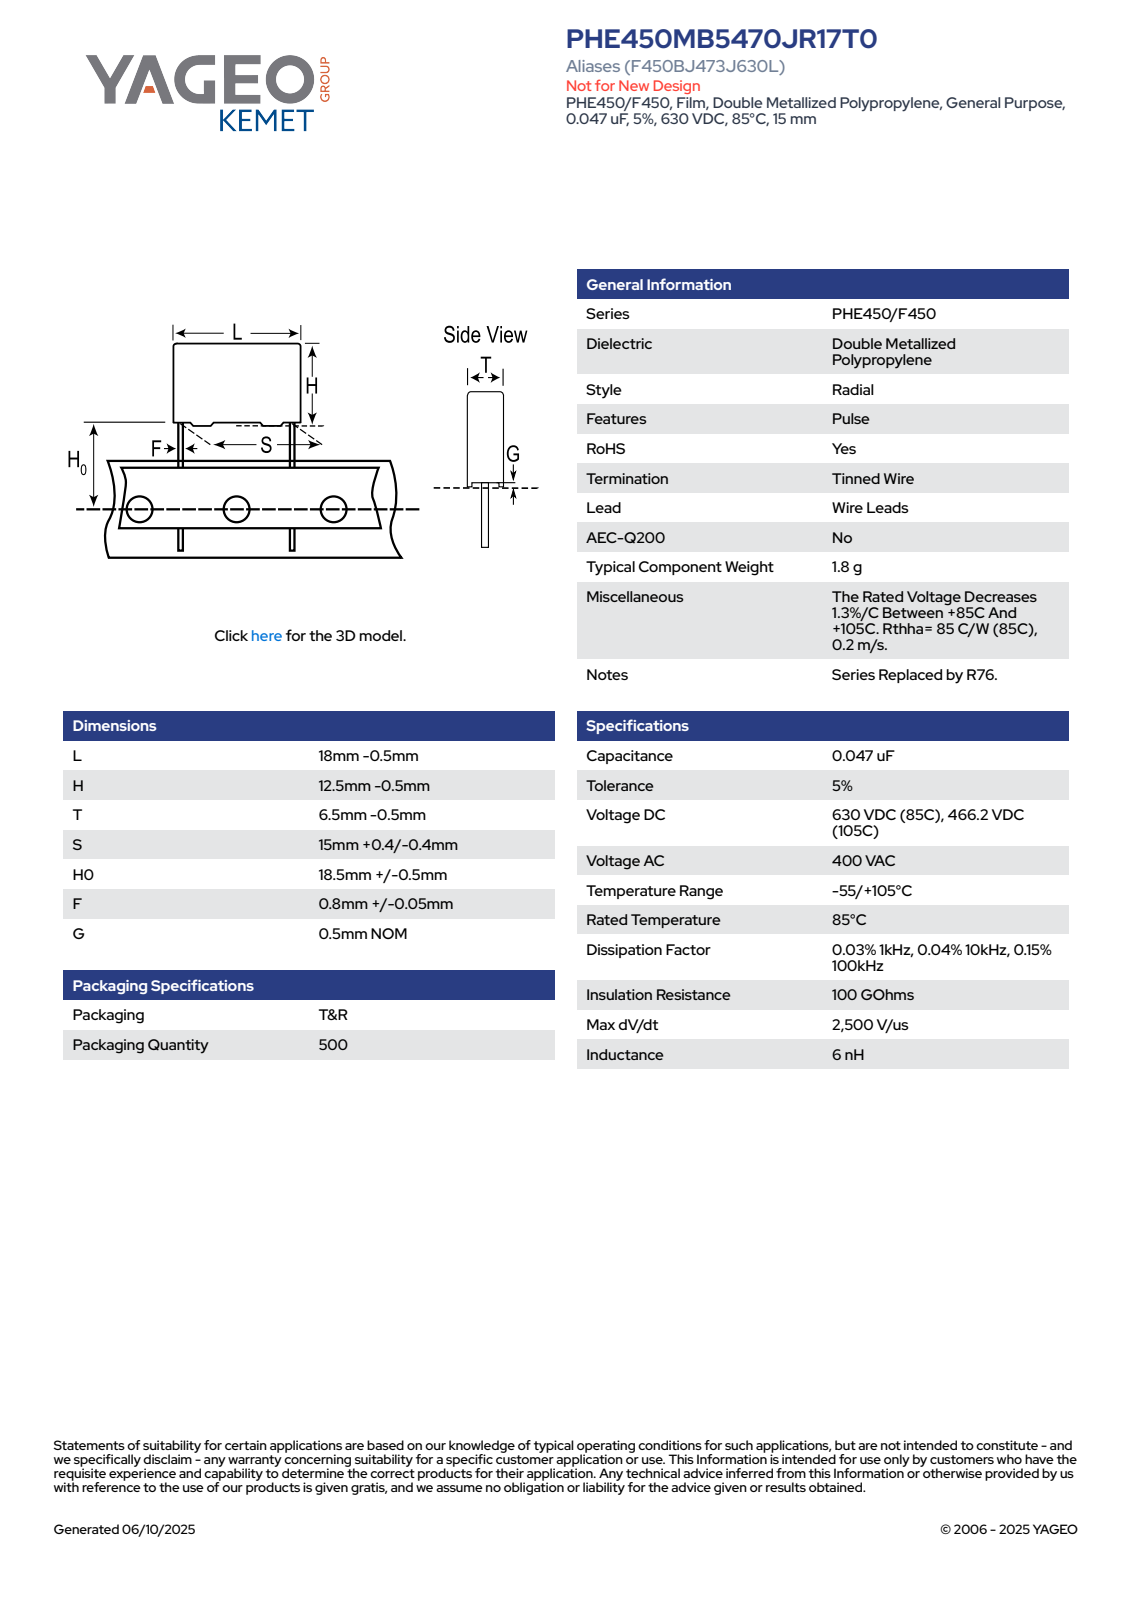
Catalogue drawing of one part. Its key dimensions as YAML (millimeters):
part_name: "CFR_RBG_18X12.5X6.5_L17.5H12T6S15H019F0.85G0.5"
step_written_by: "SolidWorks 2014 (AUTOMOTIVE_DESIGN)"
units: millimeters
bodies: {solids: 4, faces: 89, planar: 81, cylindrical: 8, other: 0}
overall_size: [31, 17.5, 6]
volume: 1229
surface_area: 890
round_bosses_or_shafts:
  - {diameter: 0.85, count: 2}
partial_cylinders:
  - {radius: 0.5, count: 4}
face_to_face_distances: [6, 11.5, 17.5, 0.34, 5.66, 0.5, 12, 5.32, 19, 19.5]
